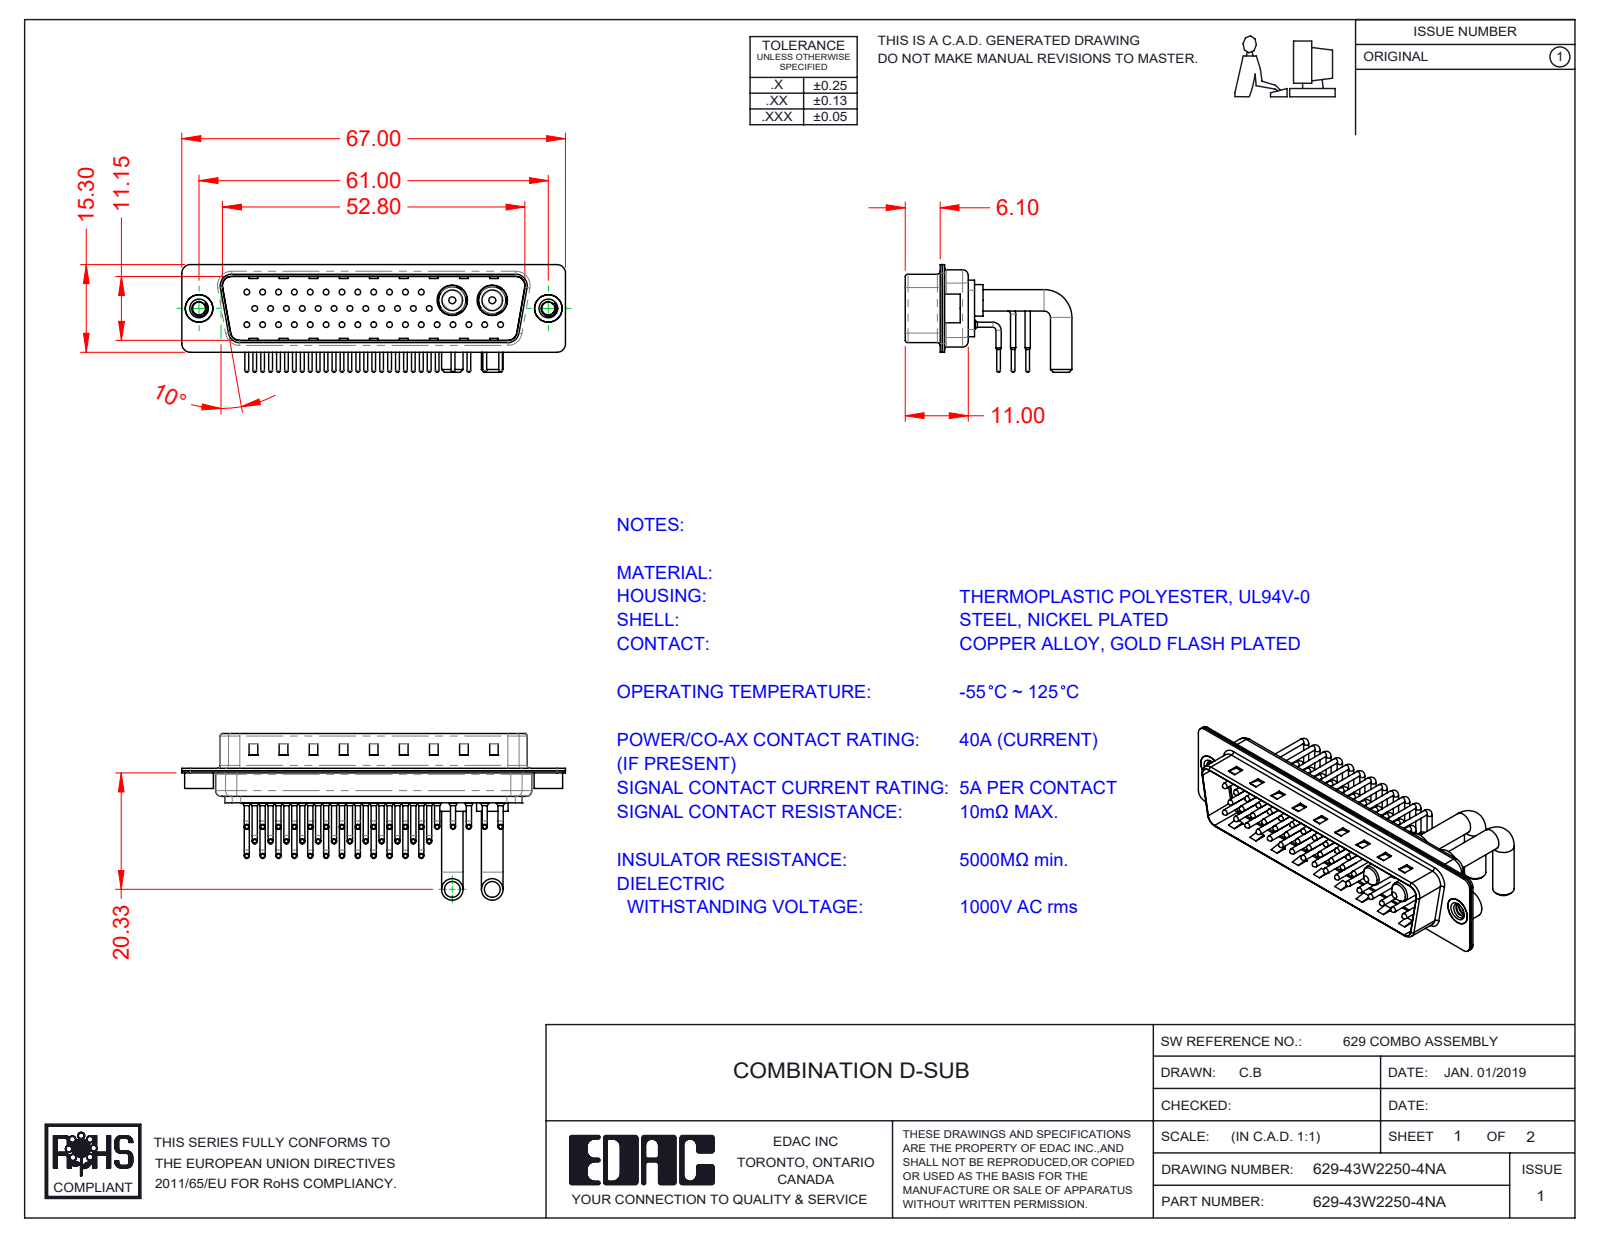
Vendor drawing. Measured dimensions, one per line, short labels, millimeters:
name: 629-43W2250-4NA; Power Pin_Ext 40A RA 50; 629Combo Shell Front_50 Contacts; 629Combo Shell Rear_50 Contacts (+5 more)
written by: SolidWorks 2020 (CONFIG_CONTROL_DESIGN)
unit: mm
bodies: 50 solids, 5008 faces (2847 planar, 1659 cylindrical, 502 other)
size: 67 × 29.11 × 18.8
volume: 5 556 mm³; area: 12 880 mm²
holes: 41× ⌀0.75, 41× ⌀1.6, 41× ⌀2, 2× ⌀2.26, 2× ⌀4, 2× ⌀4.8, 2× ⌀4.85, 2× ⌀5.3
bosses: 82× ⌀0.9, 41× ⌀1.5, 41× ⌀1, 41× ⌀0.65, 4× ⌀3.75, 2× ⌀5.5, 2× ⌀5.2, 2× ⌀5
rounds: 41× R1.01, 16× R1.5, 12× R2, 8× R0.5, 8× R1.6, 4× R0.25, 4× R0.6, 4× R0.65
face distances: 0.4, 11.55, 5.6, 4.1, 6, 0.78, 1.5, 0.77, 12.33, 1.1
hole spacings: 2.77, 5.54, 3.16, 8.31, 11.08, 13.85, 16.62, 19.39
